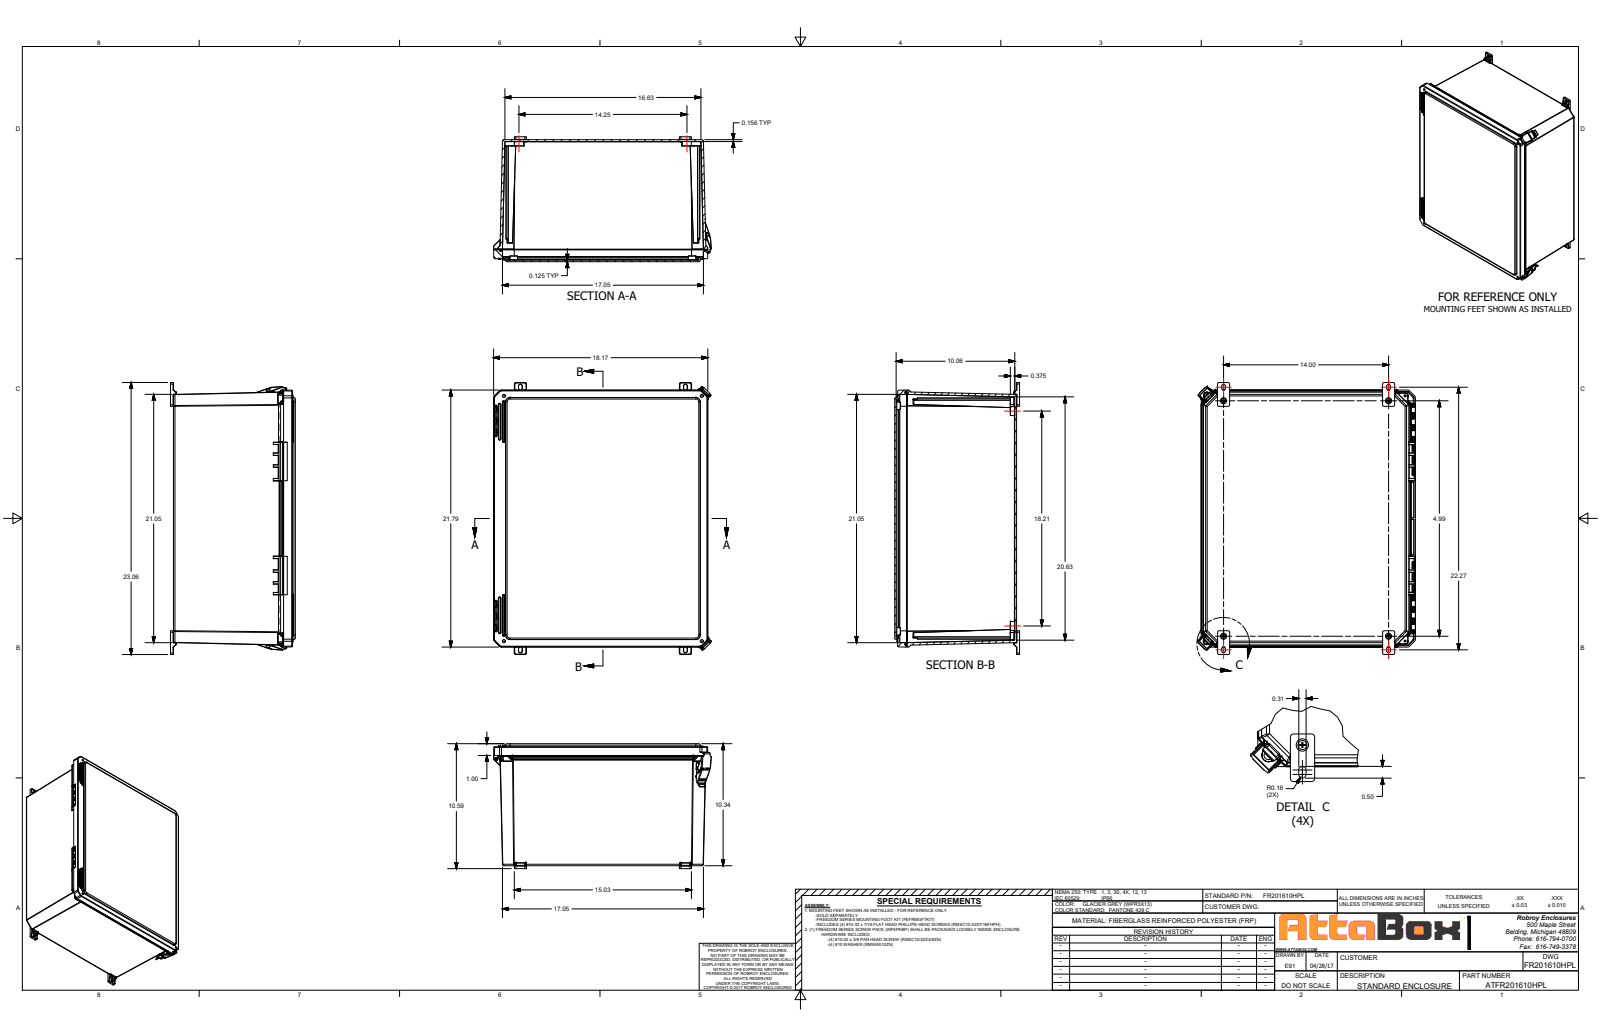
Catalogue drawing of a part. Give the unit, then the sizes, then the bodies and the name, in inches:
Units: inches
Overall size (bounding box): 22.363 × 18.461 × 10.912
Round holes (diameter × count): ⌀0.135 ×8, ⌀0.152 ×8, ⌀0.159 ×8, ⌀0.135 ×6, ⌀0.15 ×4, ⌀0.156 ×4, ⌀0.252 ×4, ⌀0.253 ×4, ⌀0.137 ×3, ⌀0.219 ×2, ⌀0.227 ×2, ⌀0.313 ×2
Round bosses / shafts (diameter × count): ⌀0.27 ×8, ⌀0.3 ×4, ⌀0.262 ×4, ⌀0.209 ×4, ⌀0.135 ×2, ⌀0.435 ×1, ⌀0.435 ×1
Partial cylindrical surfaces — rounded edges, fillets, slot ends (radius × count): R0.01 ×190, R0.005 ×110, R0.03 ×71, R0.02 ×54, R0.06 ×36, R0.09 ×26, R0.03 ×24, R0.096 ×24
Main face-to-face distances: 0.125, 0.156, 10.182, 10.338, 10.057, 10.213, 0.212, 0.209, 0.21, 0.25
Hole centre spacings: 19.56, 20.42, 0.25, 19.979, 20.788, 20.79, 14.151, 0.25
Volume: 285.3 in³ · Surface area: 3 202 in²
Bodies: 29 solids, 2479 faces (814 planar, 1059 cylindrical, 606 other)
Part name (STEP PRODUCT): FR201610HPL
STEP written by: SolidWorks 2021 (AUTOMOTIVE_DESIGN)
